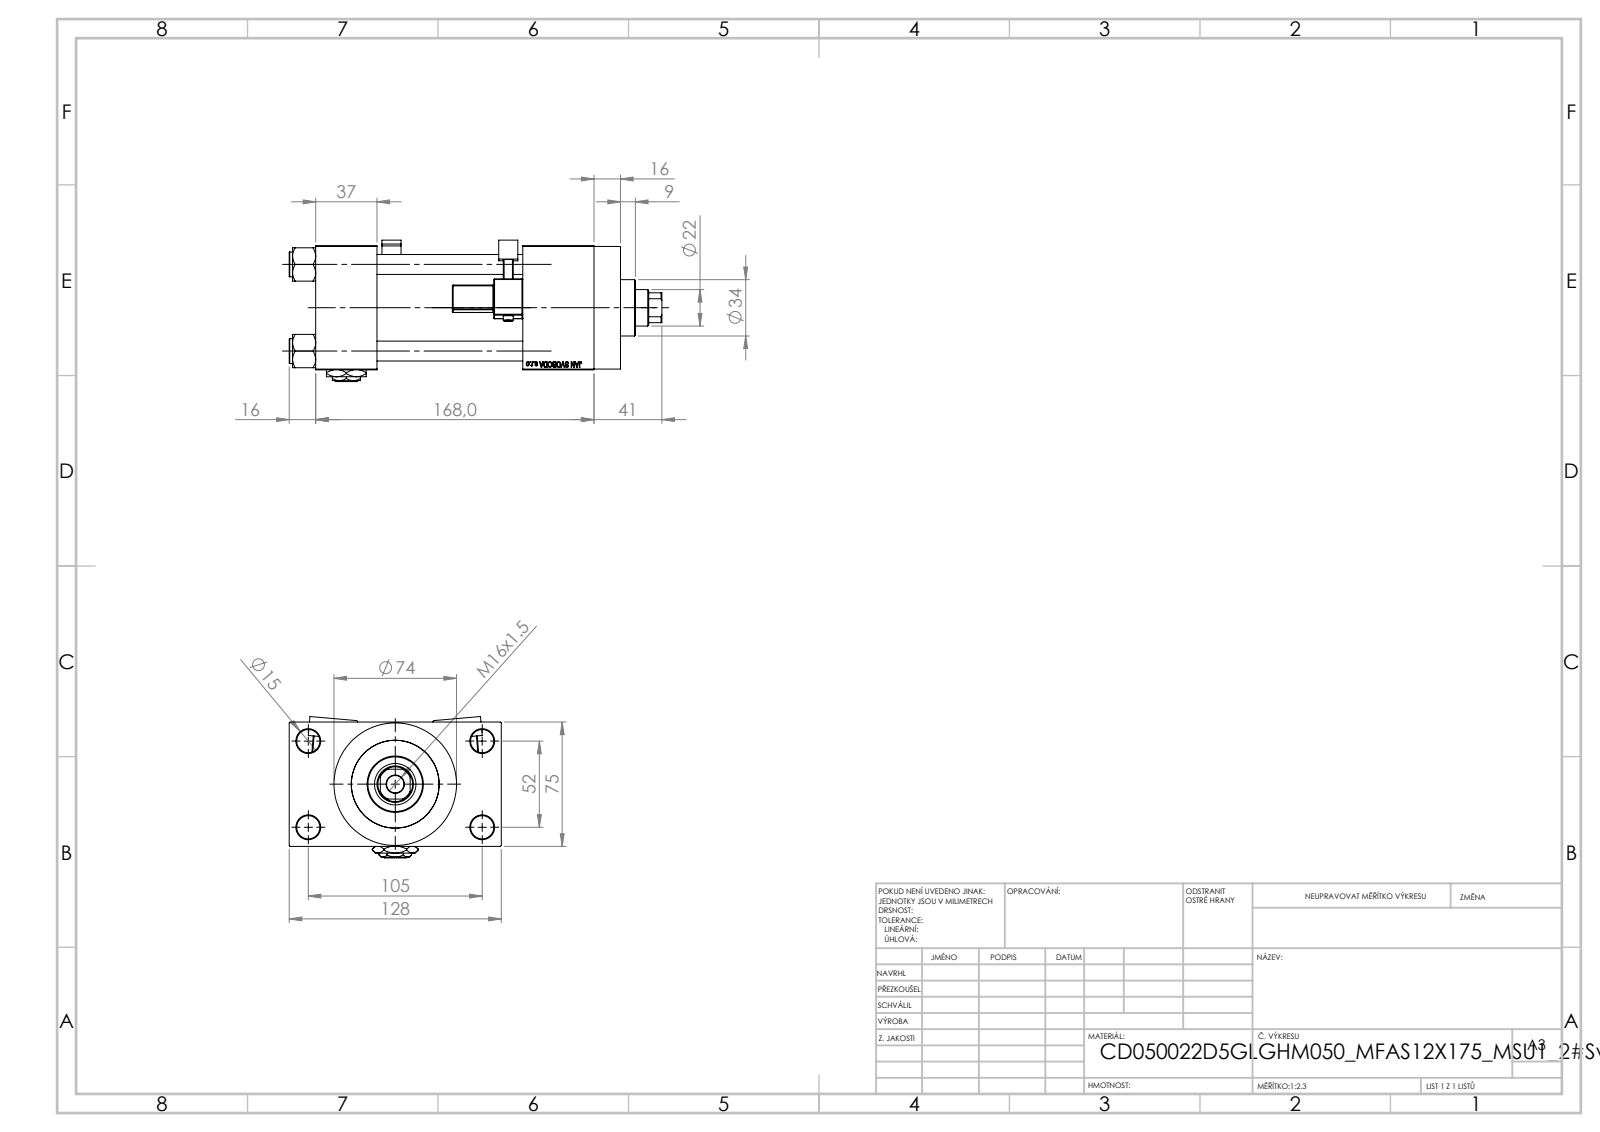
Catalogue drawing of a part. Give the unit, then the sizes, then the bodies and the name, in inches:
Units: inches
Overall size (bounding box): 8.858 × 5.039 × 3.36
Round holes (diameter × count): ⌀0.472 ×4, ⌀0.551 ×4, ⌀0.276 ×2, ⌀0.825 ×2, ⌀1.181 ×2, ⌀0.413 ×1, ⌀0.866 ×1, ⌀0.984 ×1, ⌀1.614 ×1, ⌀1.969 ×1, ⌀2.087 ×1
Round bosses / shafts (diameter × count): ⌀0.591 ×4, ⌀0.236 ×2, ⌀2.913 ×1, ⌀2.205 ×1, ⌀1.339 ×1
Partial cylindrical surfaces — rounded edges, fillets, slot ends (radius × count): R0.02 ×48, R0.039 ×2, R0.098 ×2, R0.157 ×2, R0.413 ×1
Main face-to-face distances: 2.953, 3.465, 3.996, 1.457, 4.921, 1.043, 6.614, 5.157, 1.693, 0.63
Hole centre spacings: 1.037, 1.456, 2.059, 2.3, 2.307, 3.096, 3.715, 2.047
Volume: 54.34 in³ · Surface area: 302.7 in²
Bodies: 14 solids, 1300 faces (577 planar, 149 cylindrical, 574 other)
Part name (STEP PRODUCT): V215CD_D_TYCINKA; V215CD_VCP_D; V215CD_VC_A; V215CD_NUT_M5_D (+3 more)
STEP written by: SolidWorks 2019 (CONFIG_CONTROL_DESIGN)
